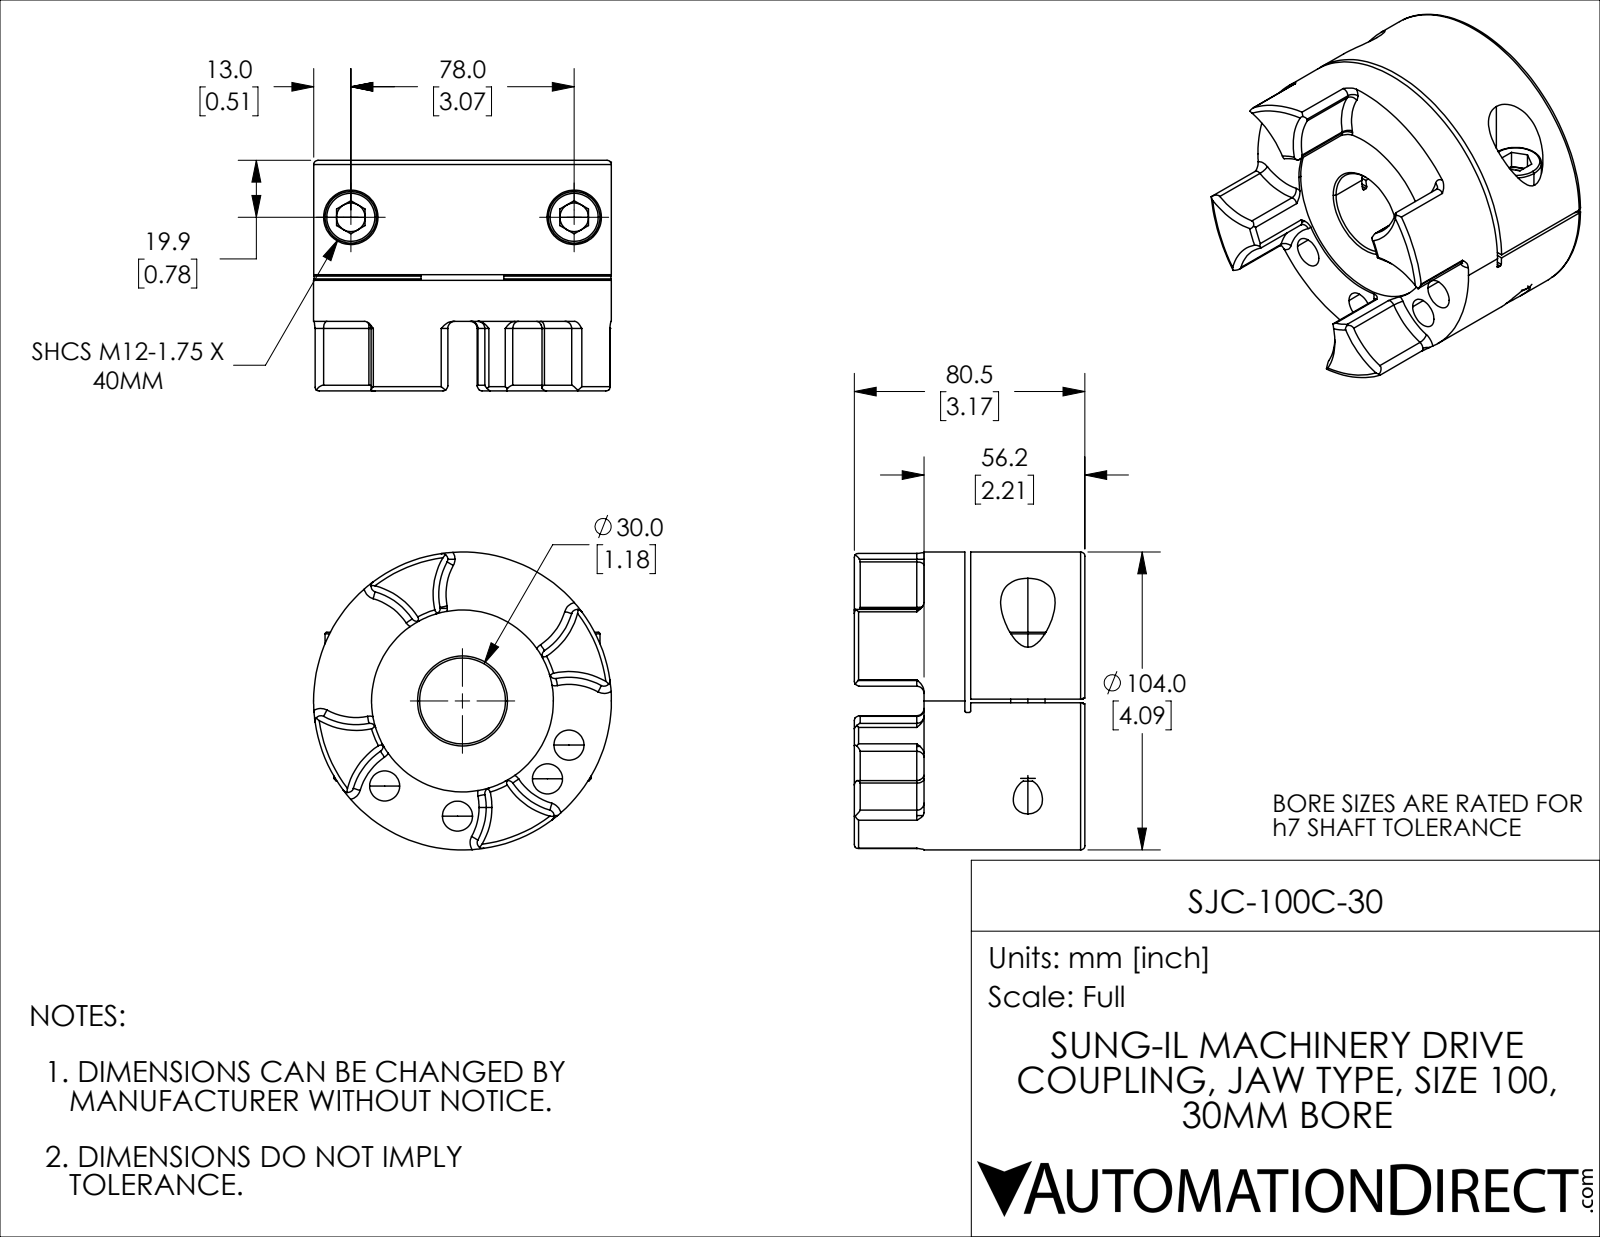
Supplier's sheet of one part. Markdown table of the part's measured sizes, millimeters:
| quantity | value |
| --- | --- |
| part name | SJC-100C-30 |
| STEP written by | SolidWorks 2021 (CONFIG_CONTROL_DESIGN) |
| units | millimeters |
| bodies | 4 solids, 222 faces (55 planar, 82 cylindrical, 85 other) |
| overall size | 104 × 104 × 80.5 |
| volume | 443 018 mm³ |
| surface area | 72 600 mm² |
| round holes (diameter × count) | 10.5 × 4, 10 × 2, 10.2 × 2, 12.5 × 2, 19 × 2, 30 × 1, 63.5 × 1 |
| round bosses / shafts (diameter × count) | 18 × 2, 12 × 2, 104 × 1 |
| partial cylindrical surfaces (radius × count) | 2 × 16, 23.68 × 4, 0.5 × 2, 75 × 1 |
| main face-to-face distances | 2, 41.9, 39.9, 56.2, 16.3, 14.3, 55.3, 15.4, 13.4, 0.9 |
| hole center spacings | 40.25, 13.98, 27.52, 34.03, 46.18, 56.92, 65.94, 78 |
